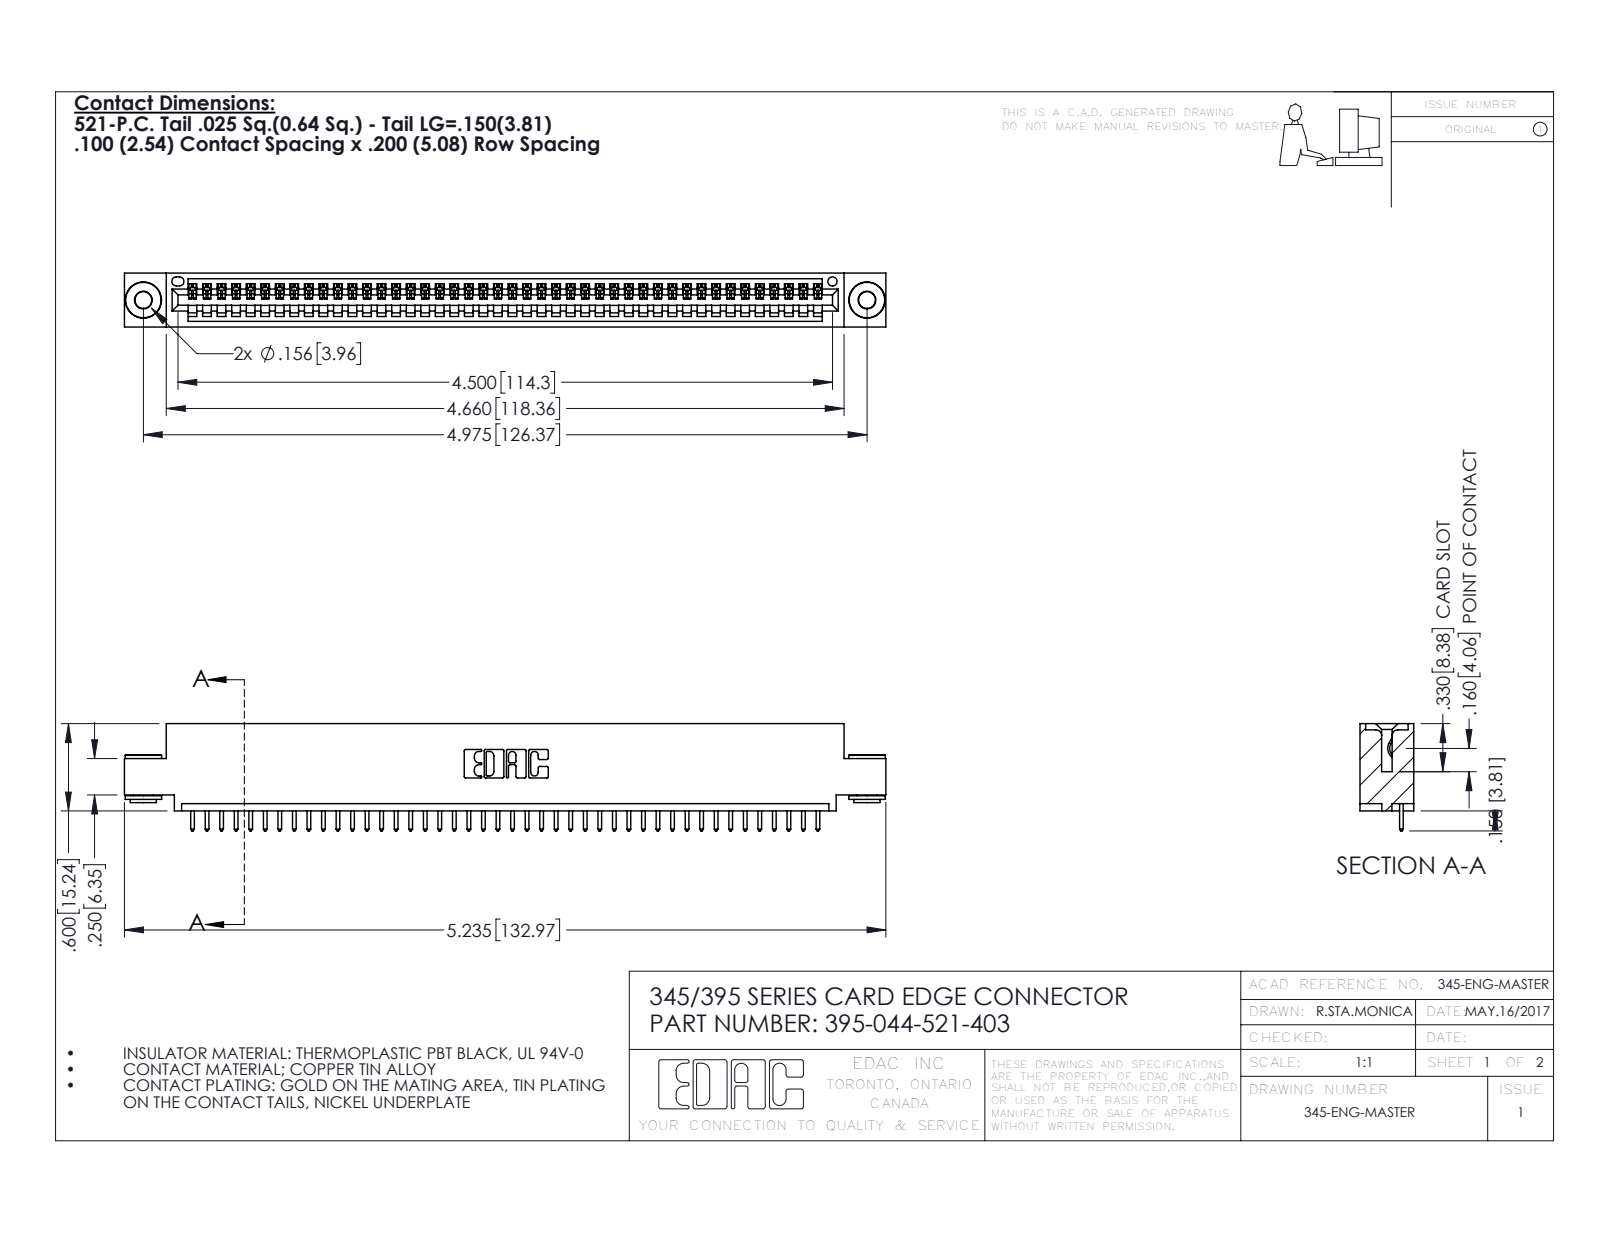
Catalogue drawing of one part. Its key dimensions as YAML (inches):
part_name: "345-250-002_345-250-002-102; 395-044-521-403; 345 Part_0.110 Offset - 0.156 Dia-TH; 345-292-001_345-293-121"
step_written_by: "SolidWorks 2016 (CONFIG_CONTROL_DESIGN)"
units: inches
bodies: {solids: 47, faces: 2720, planar: 1854, cylindrical: 858, other: 8}
overall_size: [5.235, 0.737, 0.37]
volume: 0.761
surface_area: 25.42
round_holes:
  - {diameter: 0.116, count: 2}
  - {diameter: 0.156, count: 2}
  - {diameter: 0.064, count: 1}
round_bosses_or_shafts:
  - {diameter: 0.25, count: 2}
  - {diameter: 0.18, count: 2}
  - {diameter: 0.136, count: 2}
partial_cylinders:
  - {radius: 0.006, count: 88}
  - {radius: 0.01, count: 88}
  - {radius: 0.01, count: 22}
  - {radius: 0.007, count: 6}
  - {radius: 0.031, count: 6}
  - {radius: 0.026, count: 3}
  - {radius: 0.031, count: 2}
  - {radius: 0.04, count: 2}
face_to_face_distances: [0.072, 0.298, 0.37, 0.2, 0.025, 0.098, 0.272, 0.225, 0.149, 0.072]
hole_center_spacings: [0.27, 4.739, 4.975]
